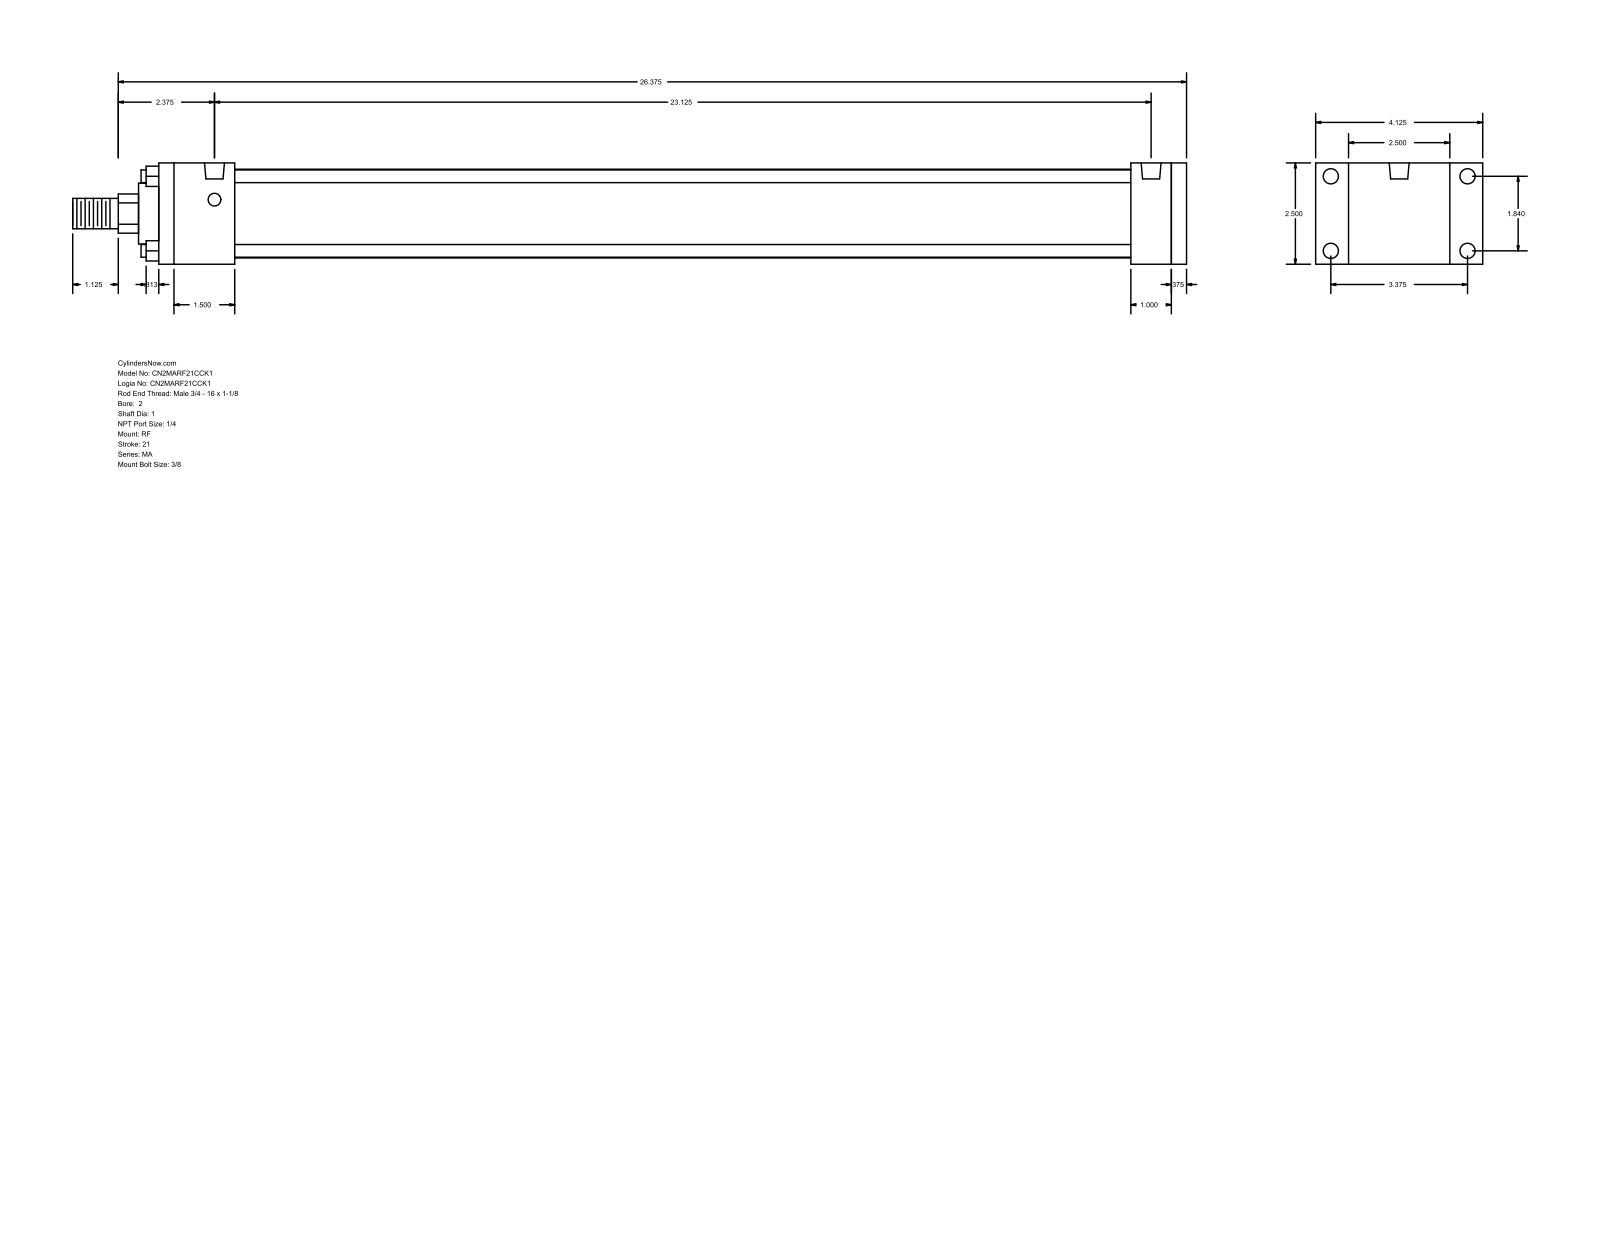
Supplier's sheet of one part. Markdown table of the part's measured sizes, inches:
| quantity | value |
| --- | --- |
| part name | MA_RF__0200_1 |
| STEP written by | GSSL Pune (CONFIG_CONTROL_DESIGN) |
| units | inches |
| bodies | 0 solids, 92 faces (64 planar, 28 cylindrical, 0 other) |
| overall size | 27.5 × 4.125 × 2.5 |
| round holes (diameter × count) | 0.313 × 4, 0.375 × 4, 0.492 × 2 |
| round bosses / shafts (diameter × count) | 0.313 × 4, 2.19 × 1, 1.5 × 1, 1 × 1, 0.75 × 1 |
| partial cylindrical surfaces (radius × count) | 0.484 × 1 |
| main face-to-face distances | 2.5, 25, 0.375, 25.375, 1, 0.813, 0.5, 1.875, 23.125, 23.5 |
| hole center spacings | 1.84, 3.375, 3.844, 23.125 |
